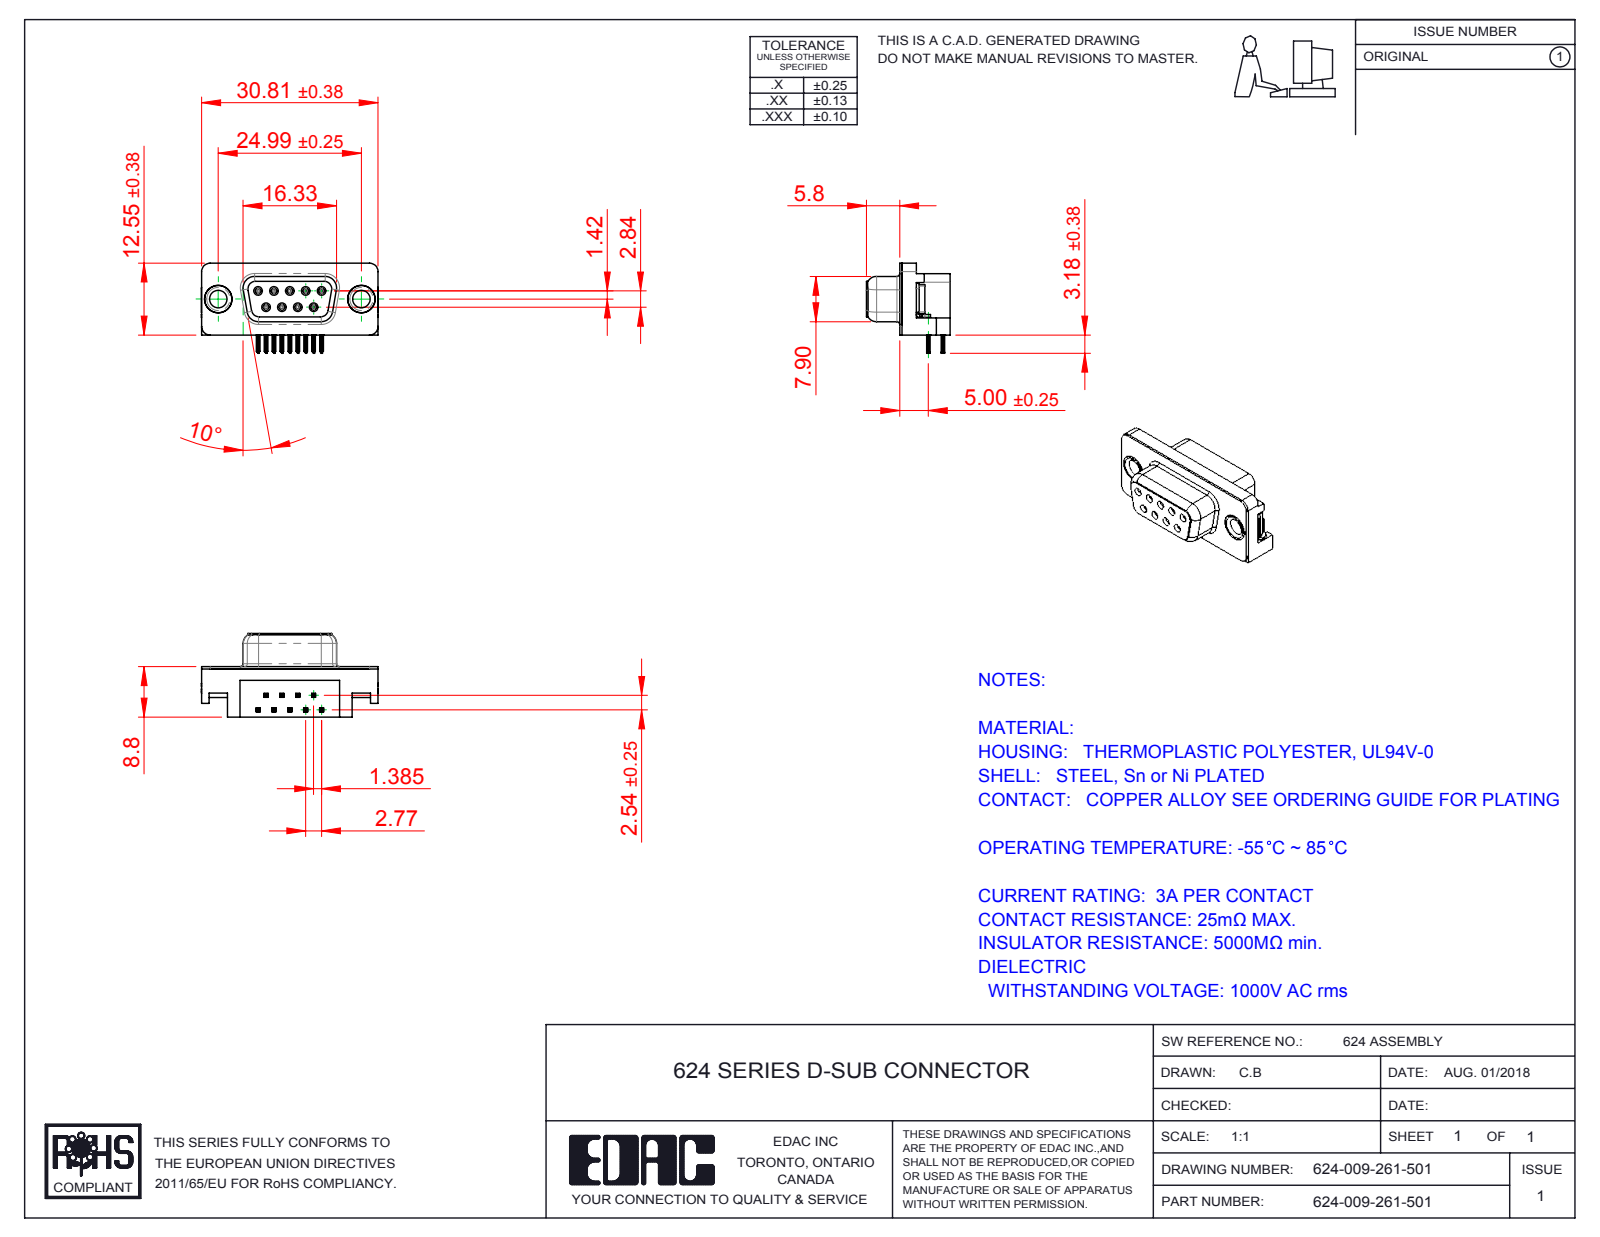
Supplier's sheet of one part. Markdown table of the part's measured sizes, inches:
| quantity | value |
| --- | --- |
| part name | 624-009-261-501; 624 Thru Hole Rivet; 624 Non Board Mount; 624 Contact Top (+3 more) |
| STEP written by | SolidWorks 2016 (CONFIG_CONTROL_DESIGN) |
| units | inches |
| bodies | 15 solids, 1480 faces (642 planar, 388 cylindrical, 450 other) |
| overall size | 1.216 × 0.619 × 0.575 |
| volume | 0.178 in³ |
| surface area | 6.682 in² |
| round holes (diameter × count) | 0.031 × 9, 0.035 × 9, 0.12 × 2, 0.157 × 2, 0.189 × 2, 0.197 × 2 |
| round bosses / shafts (diameter × count) | 0.047 × 9, 0.193 × 2, 0.187 × 2, 0.152 × 2 |
| partial cylindrical surfaces (radius × count) | 0.004 × 72, 0.006 × 36, 0.014 × 18, 0.039 × 18, 0.013 × 9, 0.01 × 8, 0.053 × 8, 0.059 × 7 |
| main face-to-face distances | 0.016, 0.331, 0.346, 0.114, 0.098, 0.244, 0.232, 0.014, 0.421, 0.407 |
| hole center spacings | 0.124, 0.109, 0.218, 0.198, 0.198, 0.327, 0.294, 0.295 |
